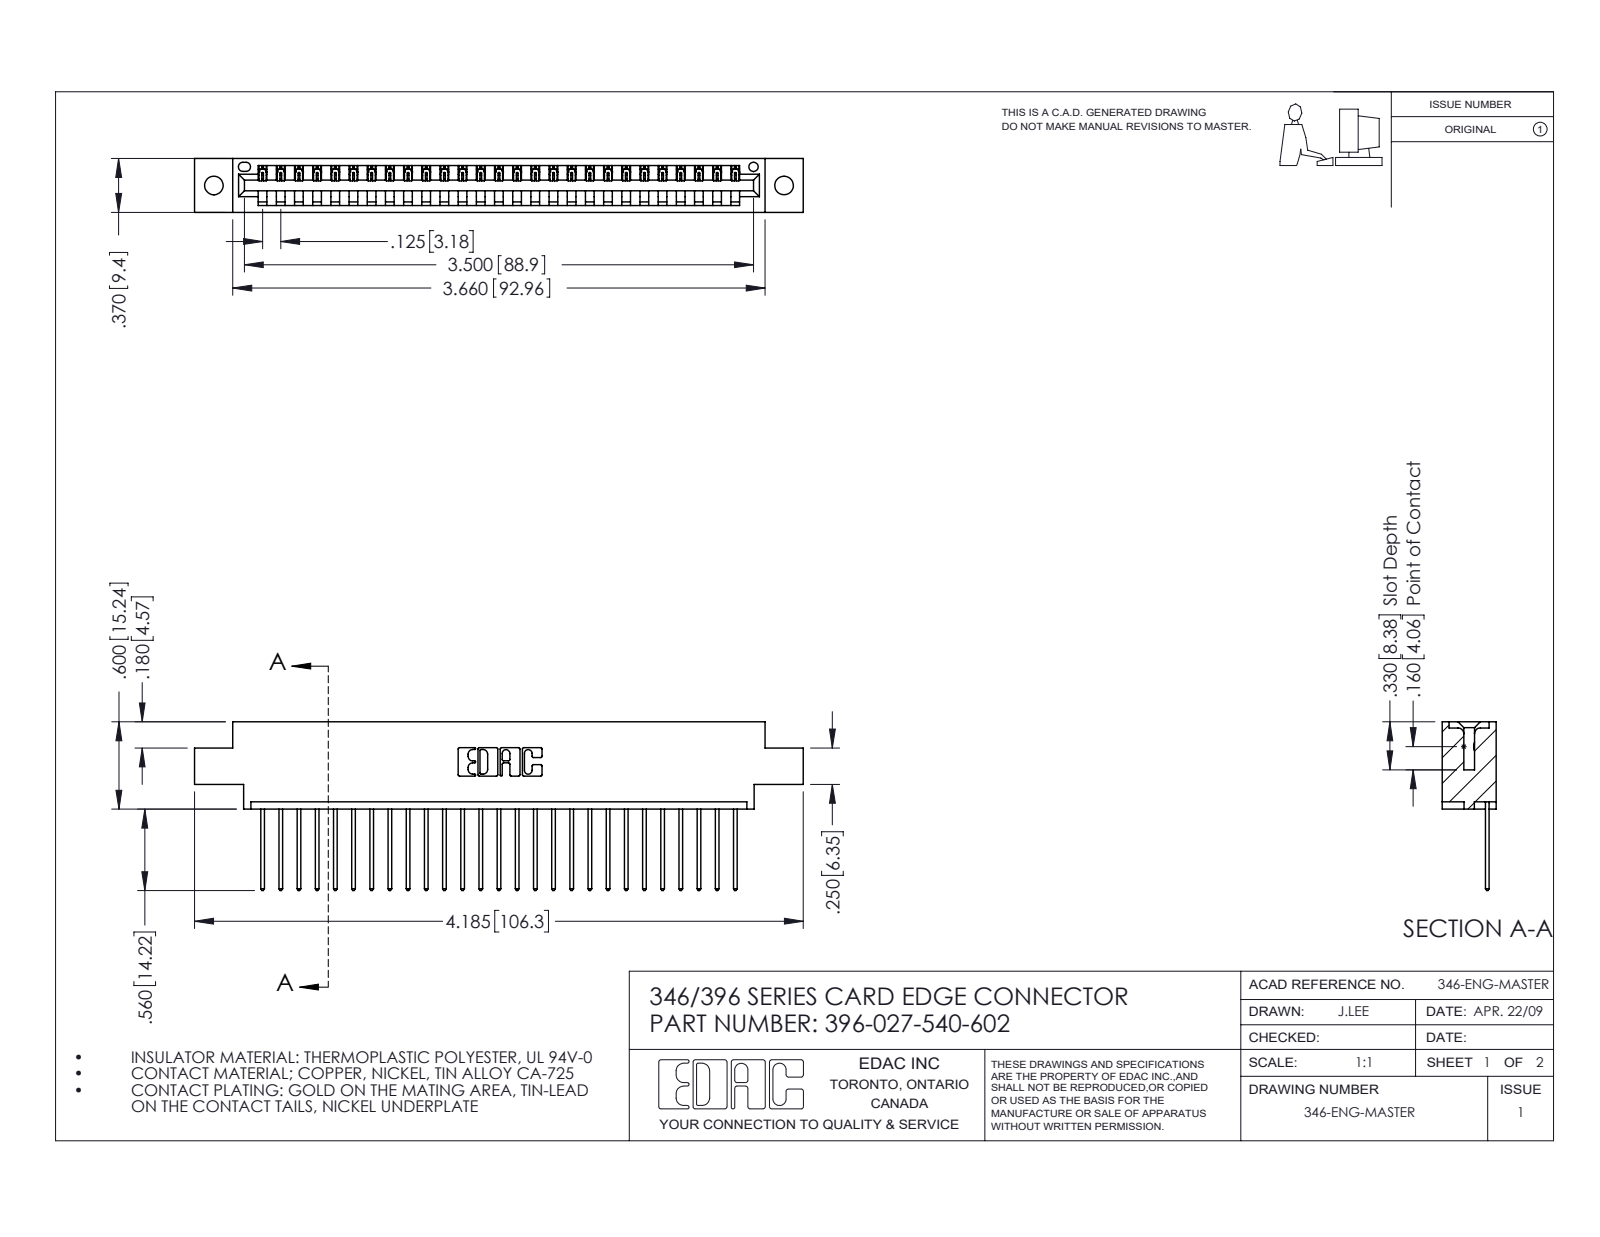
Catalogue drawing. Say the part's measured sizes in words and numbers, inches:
The part is named "396-027-540-602; 346 Part_0.170 Offset - 0.128 Dia; 345-292-001_345-293-140". Its 3-D file was written by "SolidWorks 2016 (CONFIG_CONTROL_DESIGN)". It is 28 solids with 1692 faces: 1160 planar, 532 cylindrical and 0 other. Overall it measures 4.185 by 1.16 by 0.37 inches. Its volume is 0.605 cubic inches and its surface area 19.2 square inches. Round holes: 2 of diameter 0.128, 1 of diameter 0.064. Partial cylindrical surfaces (rounded edges, fillets, slot ends): 54 of radius 0.006, 54 of radius 0.01, 22 of radius 0.01, 6 of radius 0.007, 6 of radius 0.031, 3 of radius 0.026, 2 of radius 0.031, 2 of radius 0.04. The main face-to-face distances are 0.048, 0.322, 0.37, 0.25, 0.072, 0.298, 0.025, 0.148, 0.222, 0.1. The hole center spacings are 0.246, 3.712, 3.92.
